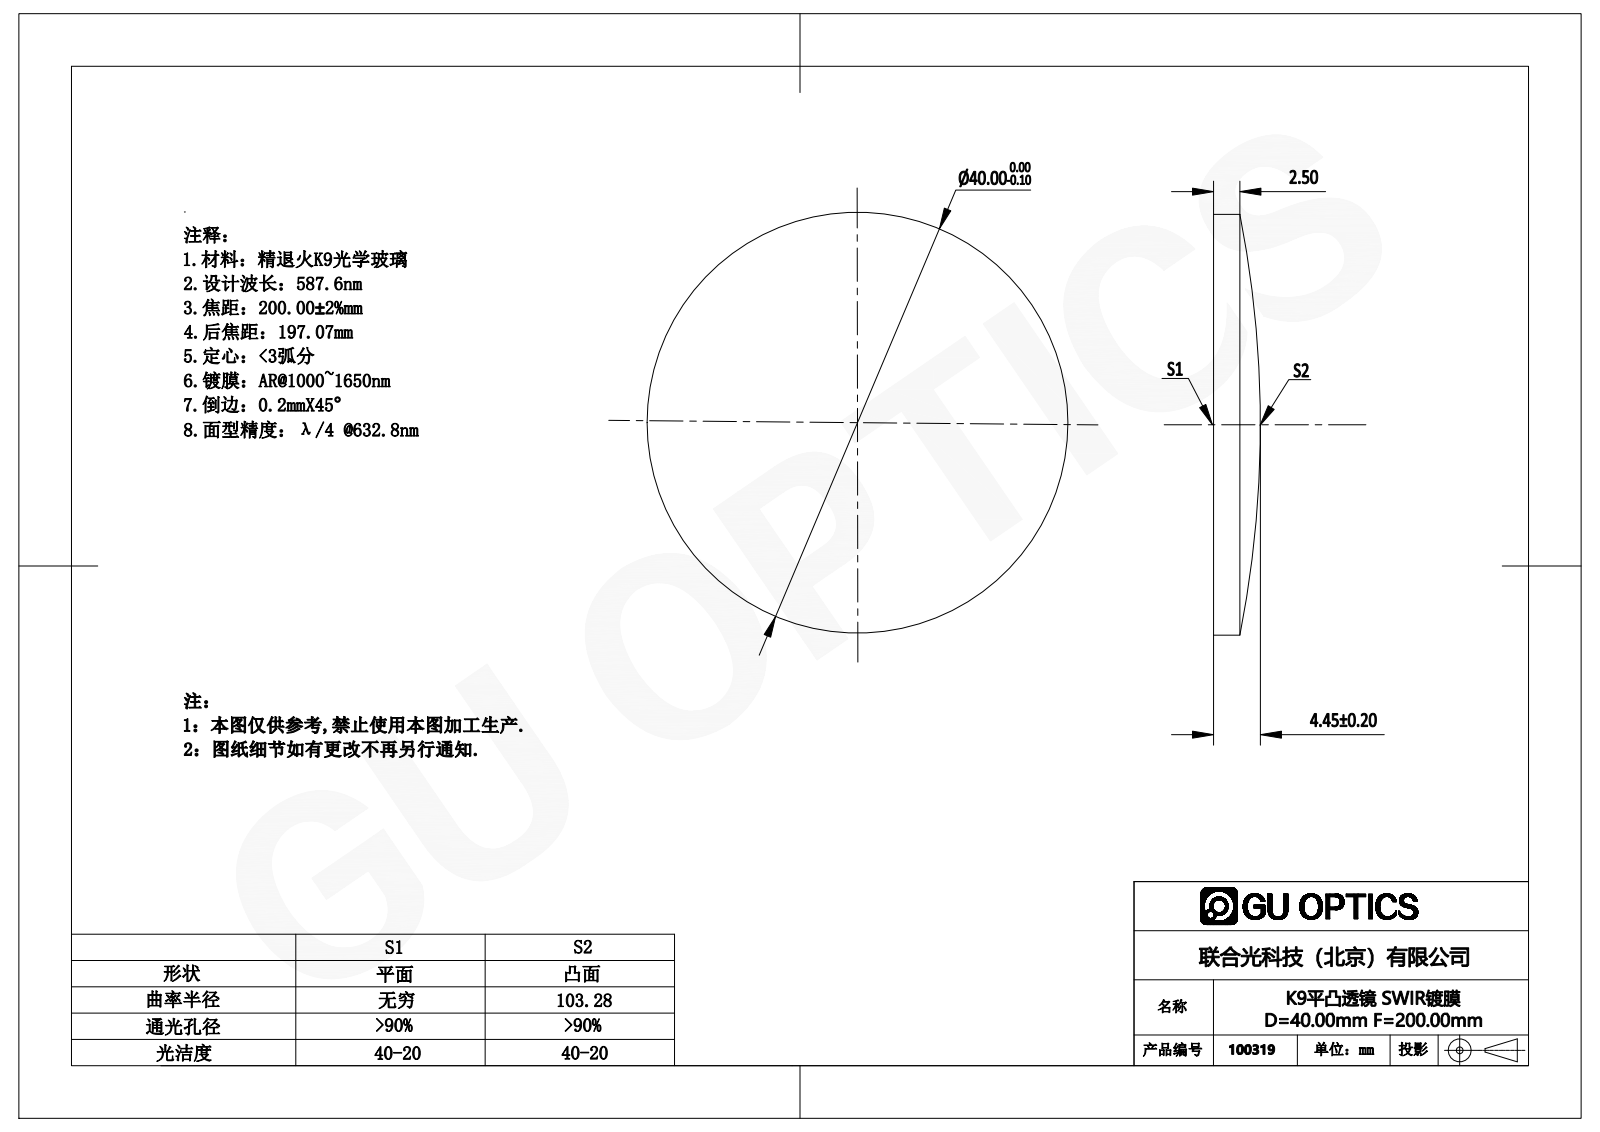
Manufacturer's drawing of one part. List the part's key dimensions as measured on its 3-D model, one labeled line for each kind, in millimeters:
Part name (STEP PRODUCT): 100147
STEP written by: SolidWorks 2016 (AUTOMOTIVE_DESIGN)
Units: millimetres
Bodies: 1 solid, 5 faces (1 planar, 2 cylindrical, 2 other)
Overall size (bounding box): 40 × 40 × 4.45
Volume: 4 371 mm³ · Surface area: 2 839 mm²
Round bosses / shafts (diameter × count): ⌀40 ×1
